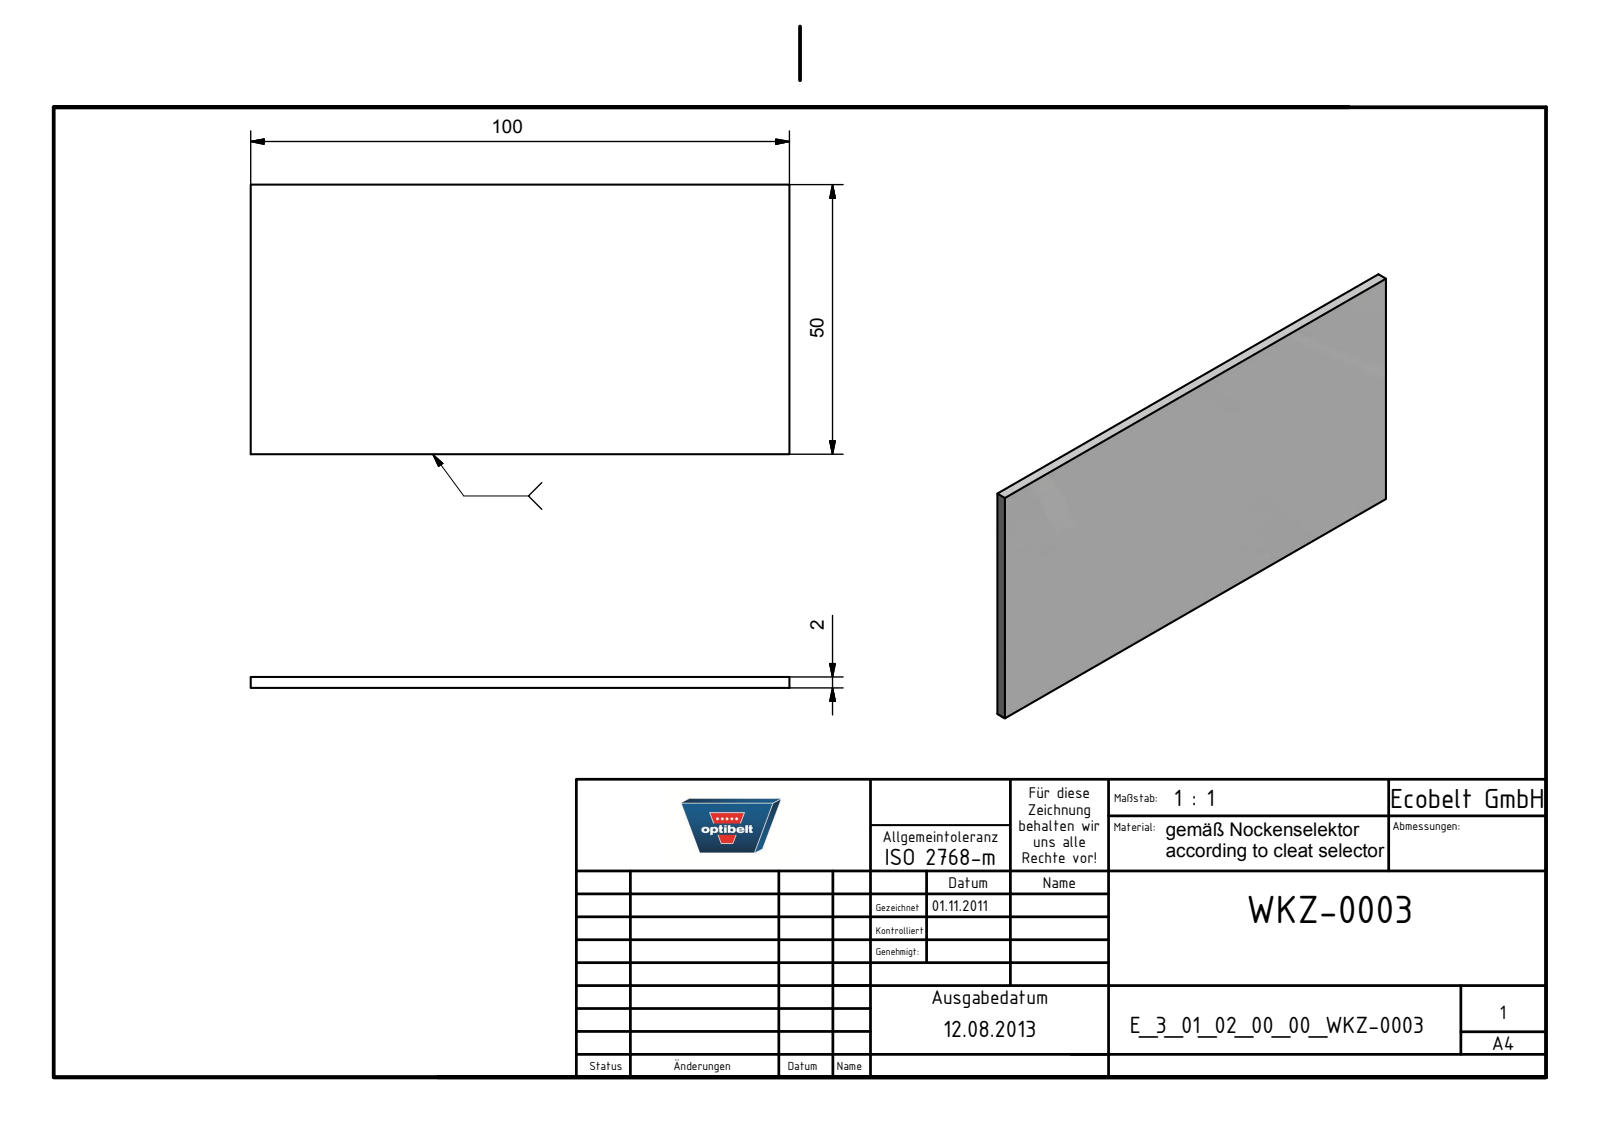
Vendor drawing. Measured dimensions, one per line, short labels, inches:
name: E_3_01_02_00_00_WKZ-0003
written by: Autodesk Inventor 2021 (AUTOMOTIVE_DESIGN)
unit: in
bodies: 1 solid, 6 faces (6 planar, 0 cylindrical, 0 other)
size: 3.937 × 1.969 × 0.079
volume: 0.61 in³; area: 16.43 in²
face distances: 0.079, 1.969, 3.937
